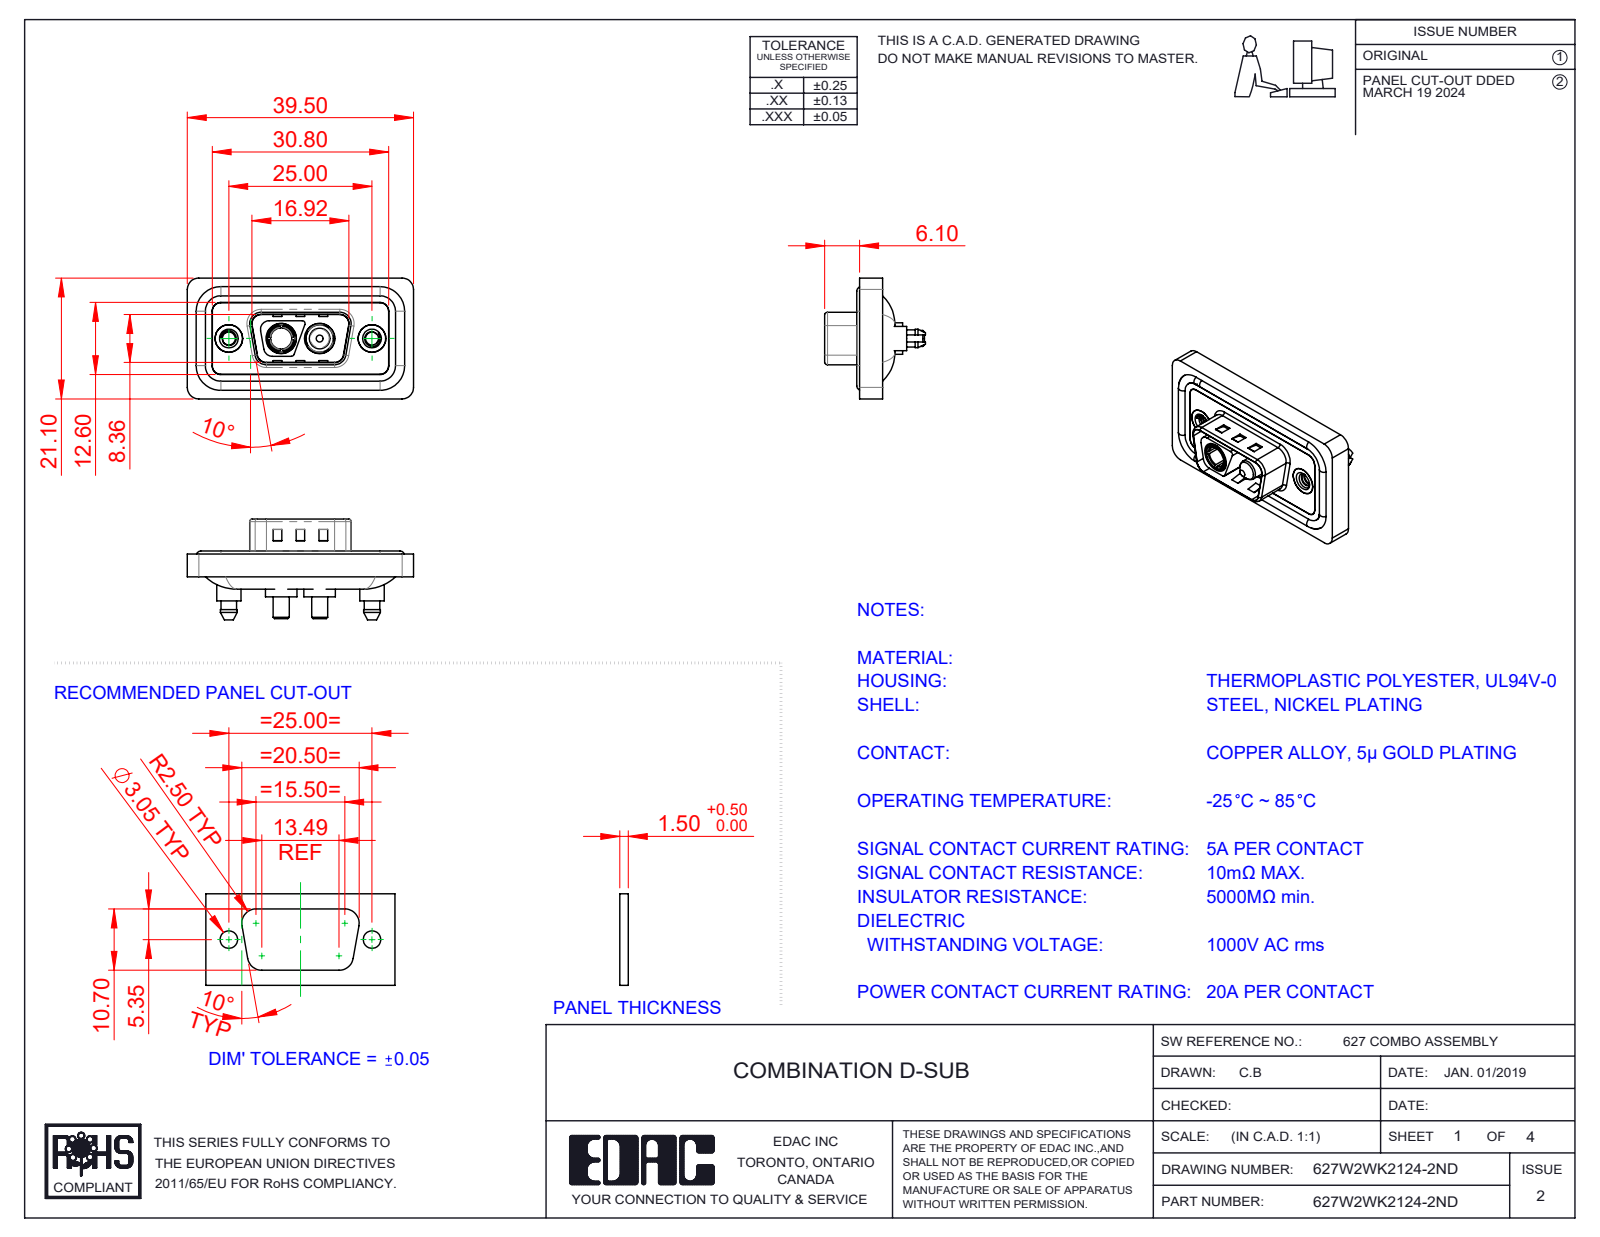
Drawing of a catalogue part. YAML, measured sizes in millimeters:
part_name: "627Combo Housing_2WK2; 627Combo Shell Rear_09 Contacts; 627Combo Shell Front_09 Contacts; 627Combo Waterproof Housing_09 Contacts (+5 more)"
step_written_by: "SolidWorks 2023 (CONFIG_CONTROL_DESIGN)"
units: millimeters
bodies: {solids: 11, faces: 592, planar: 205, cylindrical: 267, other: 120}
overall_size: [39.5, 21.1, 17.6]
volume: 4689
surface_area: 7678
round_holes:
  - {diameter: 2.26, count: 2}
  - {diameter: 4, count: 2}
  - {diameter: 4.8, count: 2}
  - {diameter: 4.85, count: 2}
  - {diameter: 5, count: 2}
  - {diameter: 5.3, count: 2}
  - {diameter: 3.7, count: 1}
round_bosses_or_shafts:
  - {diameter: 1.6, count: 4}
  - {diameter: 5.5, count: 2}
  - {diameter: 5.4, count: 2}
  - {diameter: 5.2, count: 2}
  - {diameter: 4.9, count: 2}
  - {diameter: 4.75, count: 2}
  - {diameter: 4.25, count: 2}
  - {diameter: 3.75, count: 2}
partial_cylinders:
  - {radius: 1.5, count: 26}
  - {radius: 2, count: 18}
  - {radius: 0.5, count: 10}
  - {radius: 1.6, count: 10}
  - {radius: 0.25, count: 4}
  - {radius: 0.6, count: 4}
  - {radius: 0.65, count: 4}
  - {radius: 0.9, count: 4}
face_to_face_distances: [0.4, 1.1, 2.9, 3.1, 0.5, 1.6, 1.5, 4, 1.8, 3.2]
hole_center_spacings: [9.14, 15.86, 6.72, 25]
